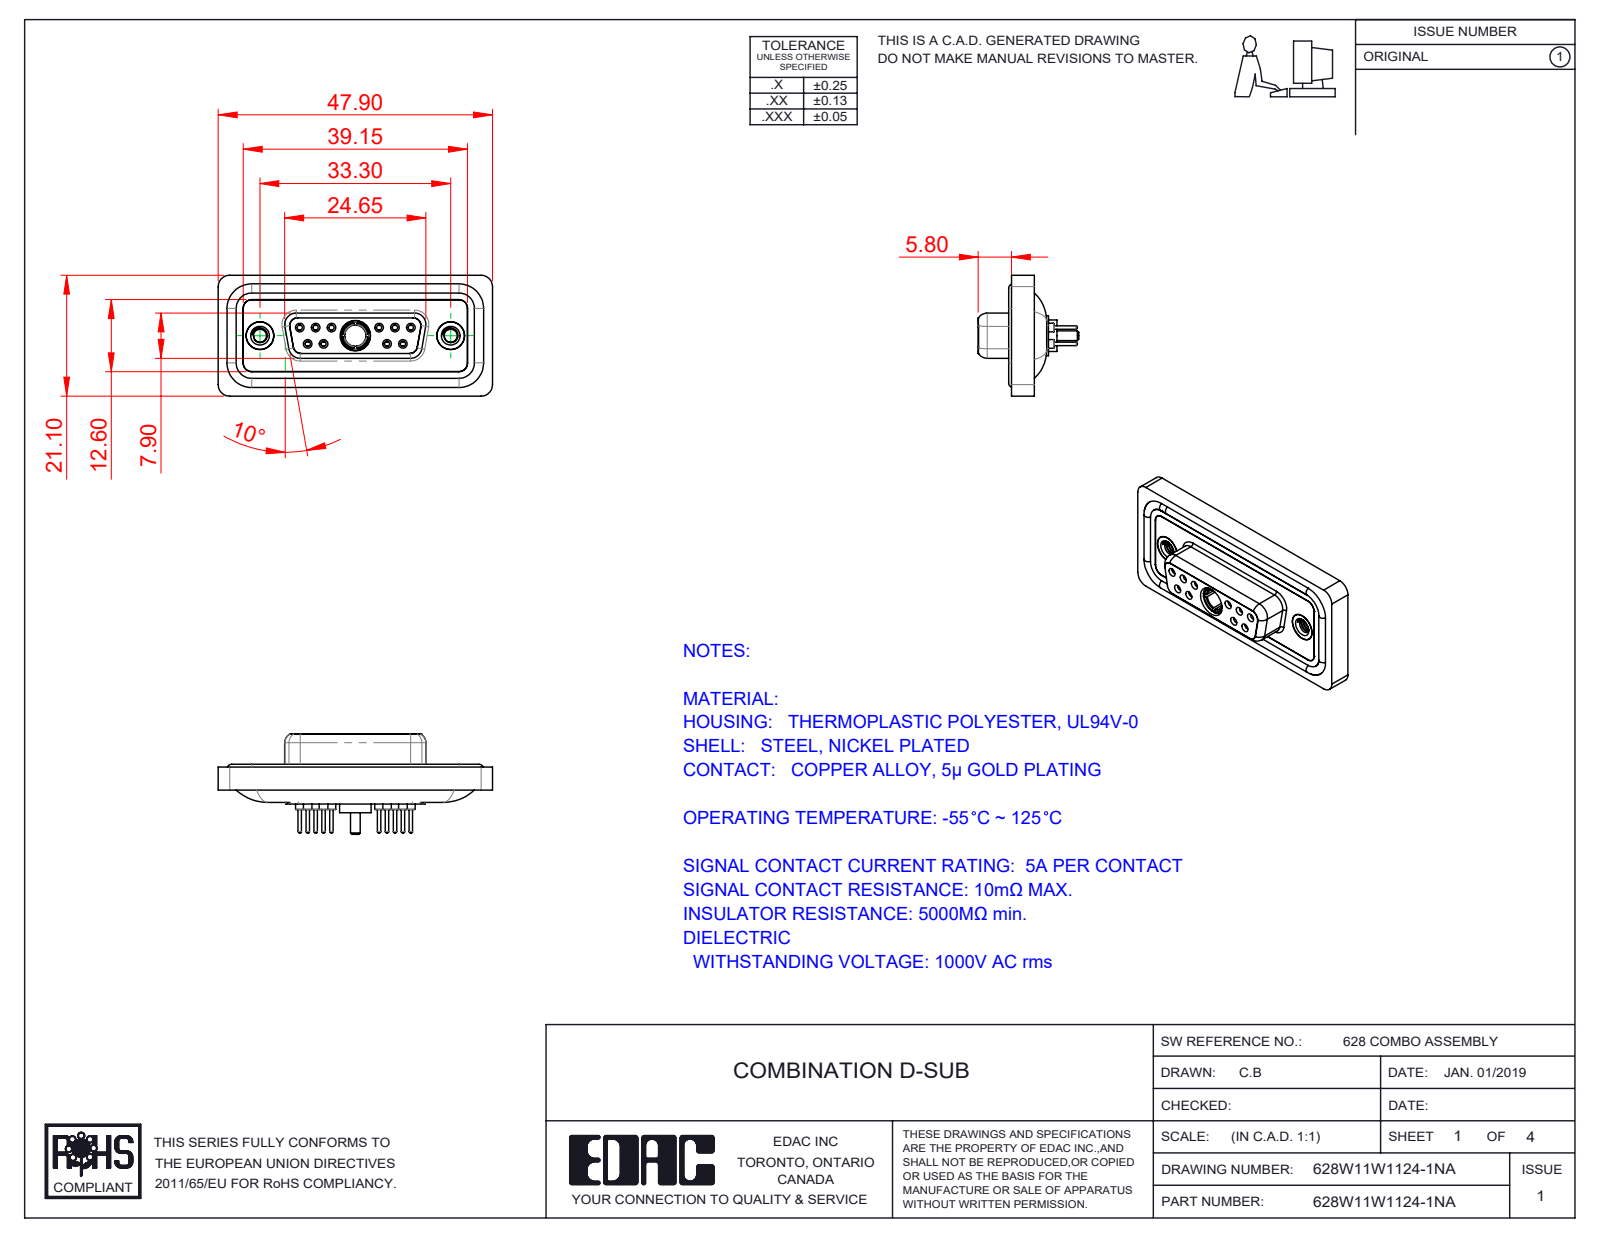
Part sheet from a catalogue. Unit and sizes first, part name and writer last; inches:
Units: inches
Overall size (bounding box): 1.886 × 0.831 × 0.691
Round holes (diameter × count): ⌀0.035 ×10, ⌀0.043 ×10, ⌀0.059 ×10, ⌀0.079 ×10, ⌀0.067 ×6, ⌀0.063 ×4, ⌀0.191 ×3, ⌀0.089 ×2, ⌀0.157 ×2, ⌀0.159 ×2, ⌀0.197 ×2, ⌀0.146 ×1
Round bosses / shafts (diameter × count): ⌀0.087 ×10, ⌀0.063 ×10, ⌀0.024 ×10, ⌀0.195 ×2, ⌀0.189 ×2, ⌀0.217 ×1, ⌀0.205 ×1, ⌀0.195 ×1
Partial cylindrical surfaces — rounded edges, fillets, slot ends (radius × count): R0.059 ×22, R0.079 ×20, R0.053 ×12, R0.063 ×8, R0.01 ×4, R0.02 ×4, R0.024 ×4, R0.026 ×4
Main face-to-face distances: 0.016, 0.063, 0.071, 0.114, 0.02, 0.043, 0.222, 0.293, 0.26, 0.278
Hole centre spacings: 0.124, 0.109, 0.545, 0.436, 0.654, 0.198, 0.198, 0.218
Volume: 0.373 in³ · Surface area: 15.53 in²
Bodies: 19 solids, 1008 faces (284 planar, 403 cylindrical, 321 other)
Part name (STEP PRODUCT): 628Combo Contact Row 2_24; 628Combo Waterproof Housing_15 Contacts; Power Socket_10A S; 628Combo Shell Rear_15 Contacts (+5 more)
STEP written by: SolidWorks 2020 (CONFIG_CONTROL_DESIGN)
